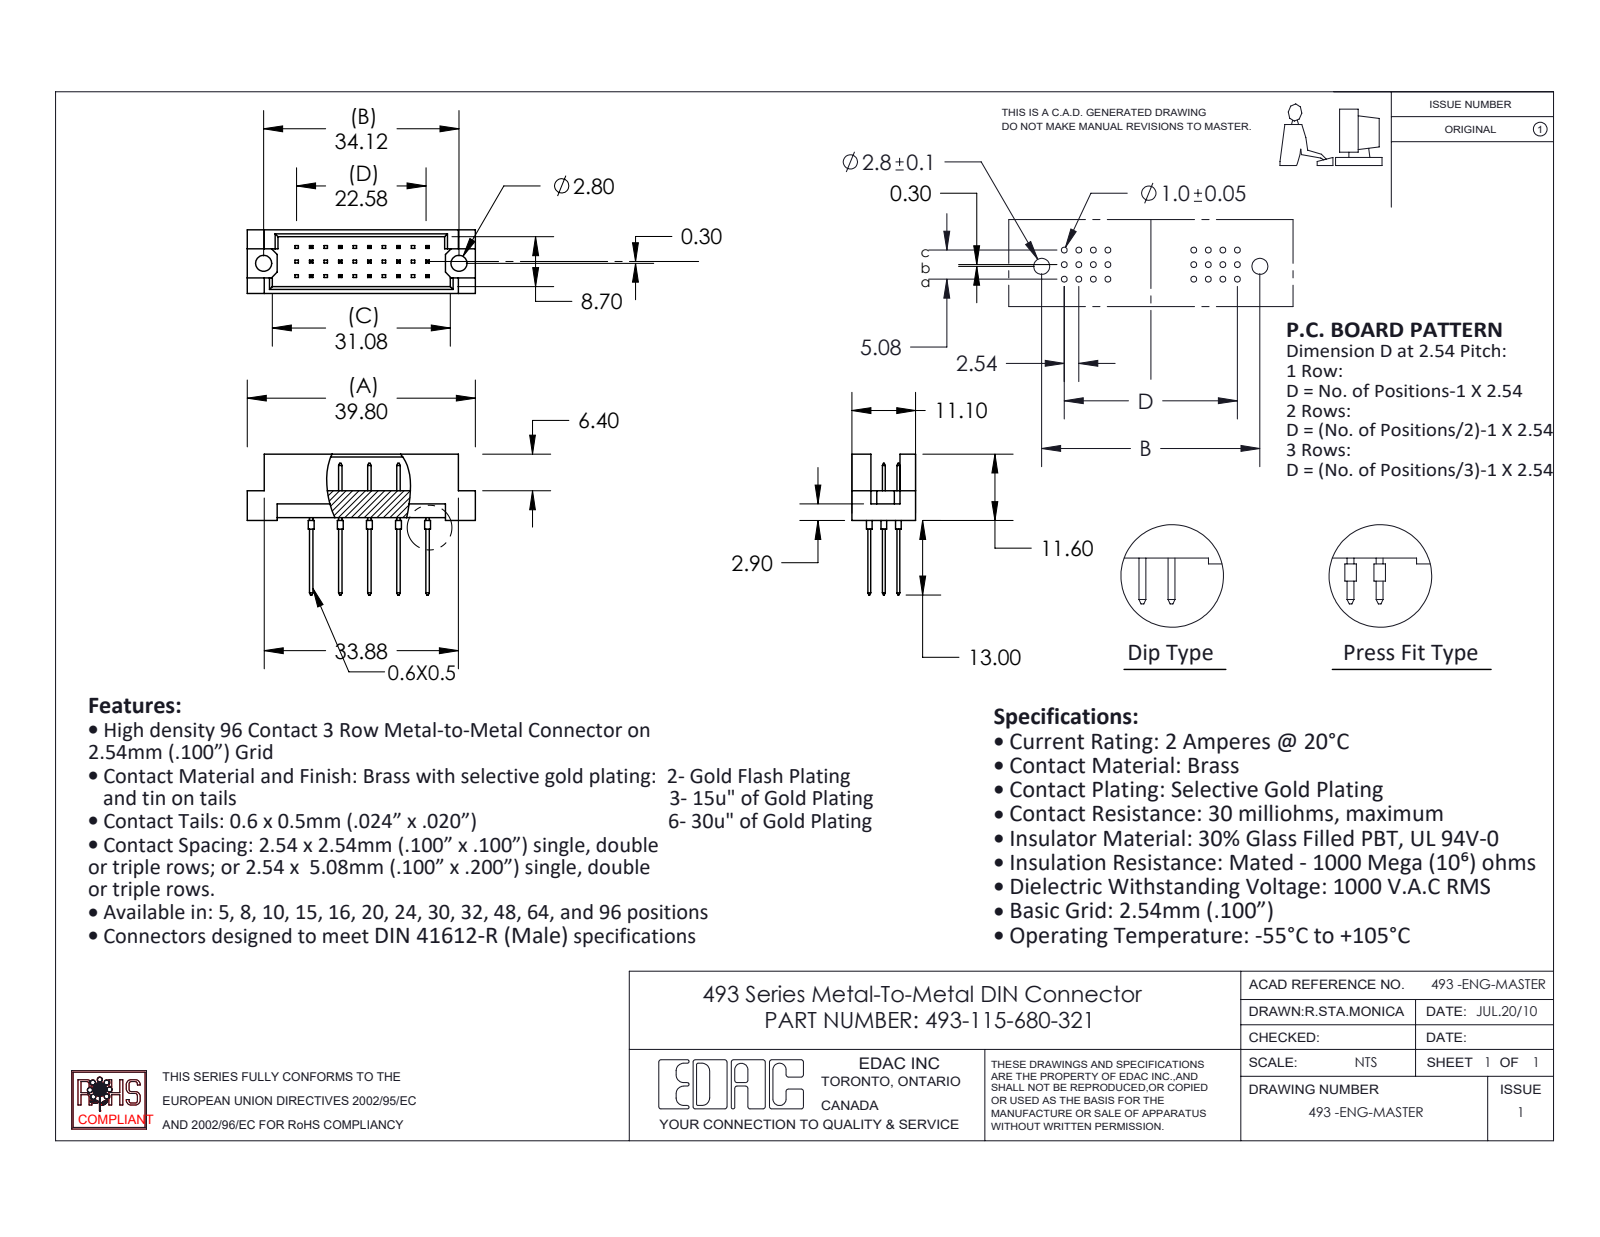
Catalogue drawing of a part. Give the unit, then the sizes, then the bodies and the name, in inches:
Units: inches
Overall size (bounding box): 1.567 × 0.969 × 0.437
Round holes (diameter × count): ⌀0.11 ×2
Round bosses / shafts (diameter × count): ⌀0.039 ×15
Main face-to-face distances: 0.2, 0.047, 0.39, 0.437, 0.02, 0.1, 0.343, 0.185, 0.4, 0.024
Hole centre spacings: 1.343
Volume: 0.152 in³ · Surface area: 5.467 in²
Bodies: 16 solids, 502 faces (468 planar, 34 cylindrical, 0 other)
Part name (STEP PRODUCT): 493-290_80; 493 Part_30; 493-115-680-322
STEP written by: SolidWorks 2020 (CONFIG_CONTROL_DESIGN)
